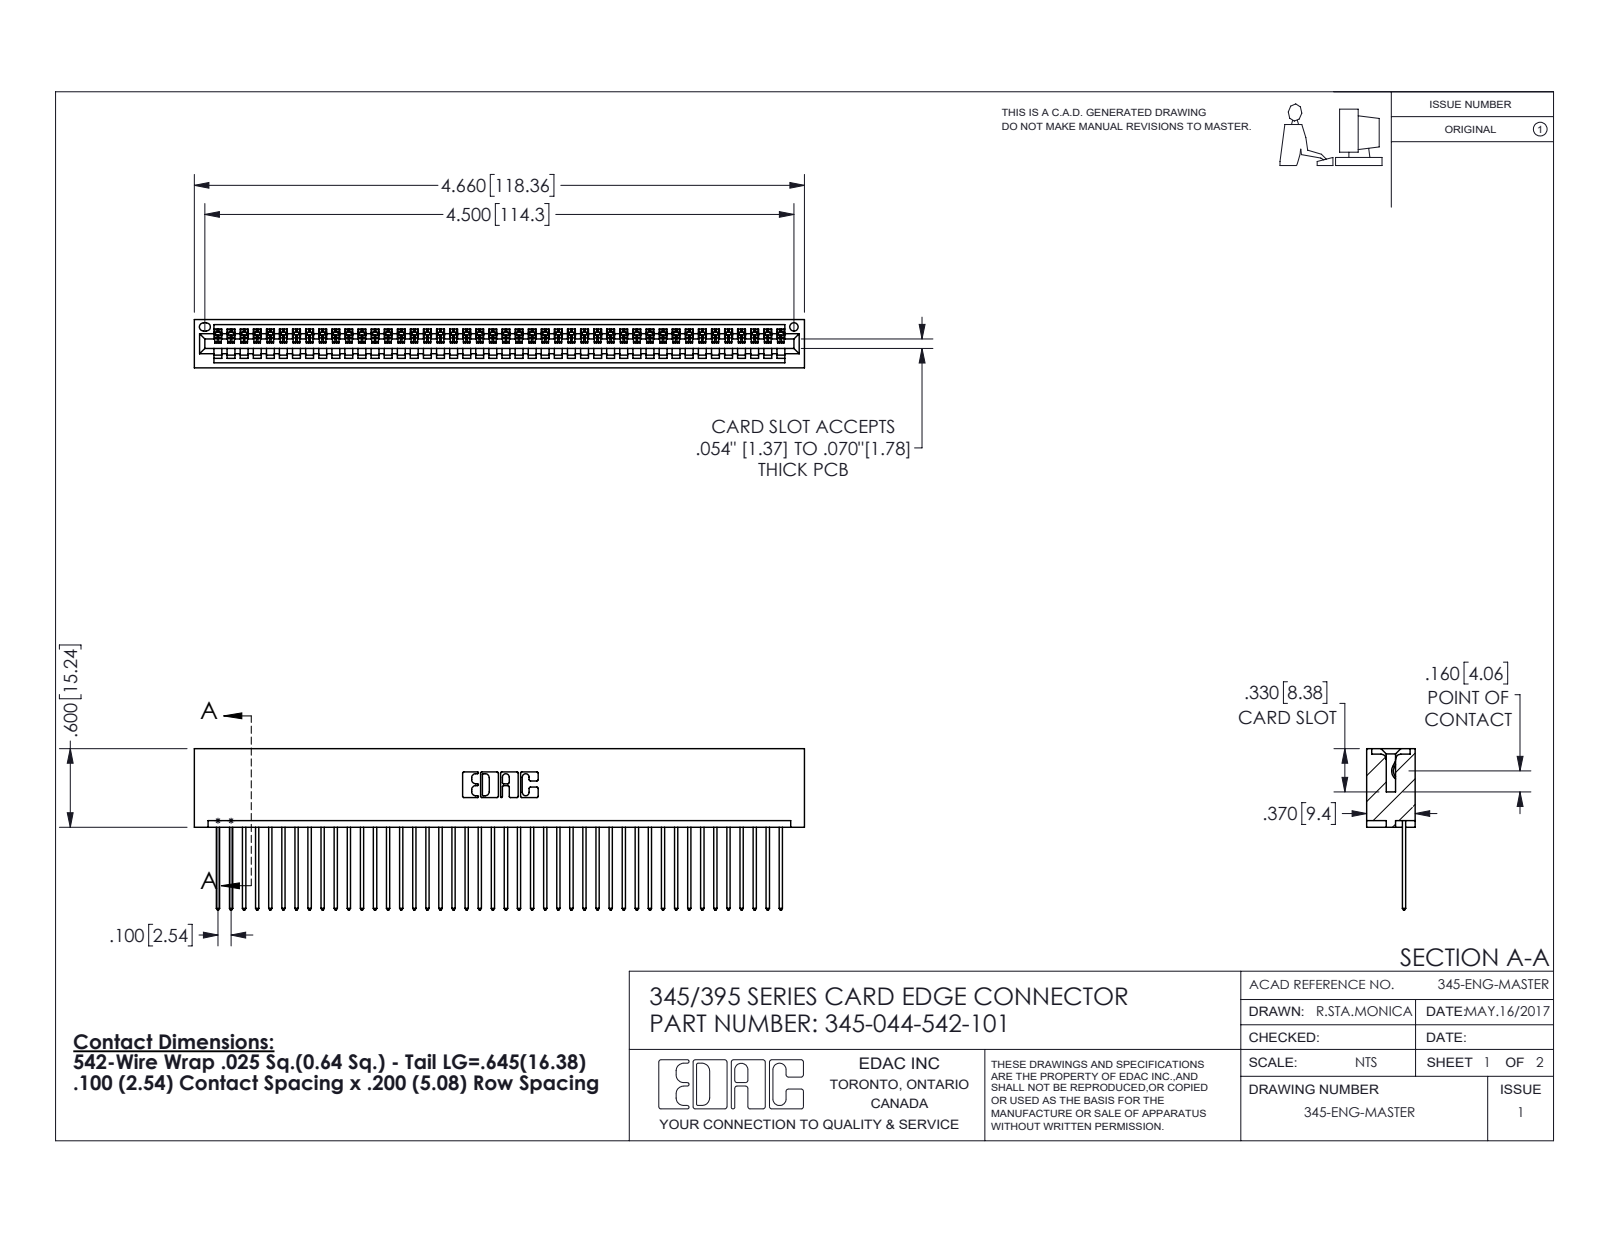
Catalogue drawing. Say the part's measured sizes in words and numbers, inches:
The part is named "345-044-542-101; 345-292-001_345-293-142; 345 Part_No Mounting Lugs". Its 3-D file was written by "SolidWorks 2016 (CONFIG_CONTROL_DESIGN)". It is 45 solids with 2670 faces: 1836 planar, 834 cylindrical and 0 other. Overall it measures 4.66 by 1.232 by 0.37 inches. Its volume is 0.729 cubic inches and its surface area 25.89 square inches. Round holes: 1 of diameter 0.064. Partial cylindrical surfaces (rounded edges, fillets, slot ends): 88 of radius 0.006, 88 of radius 0.01, 22 of radius 0.01, 6 of radius 0.007, 6 of radius 0.031, 3 of radius 0.026, 2 of radius 0.031, 2 of radius 0.04. The main face-to-face distances are 0.072, 0.298, 0.098, 0.272, 0.025, 0.37, 0.2, 0.225, 0.149, 0.072.
